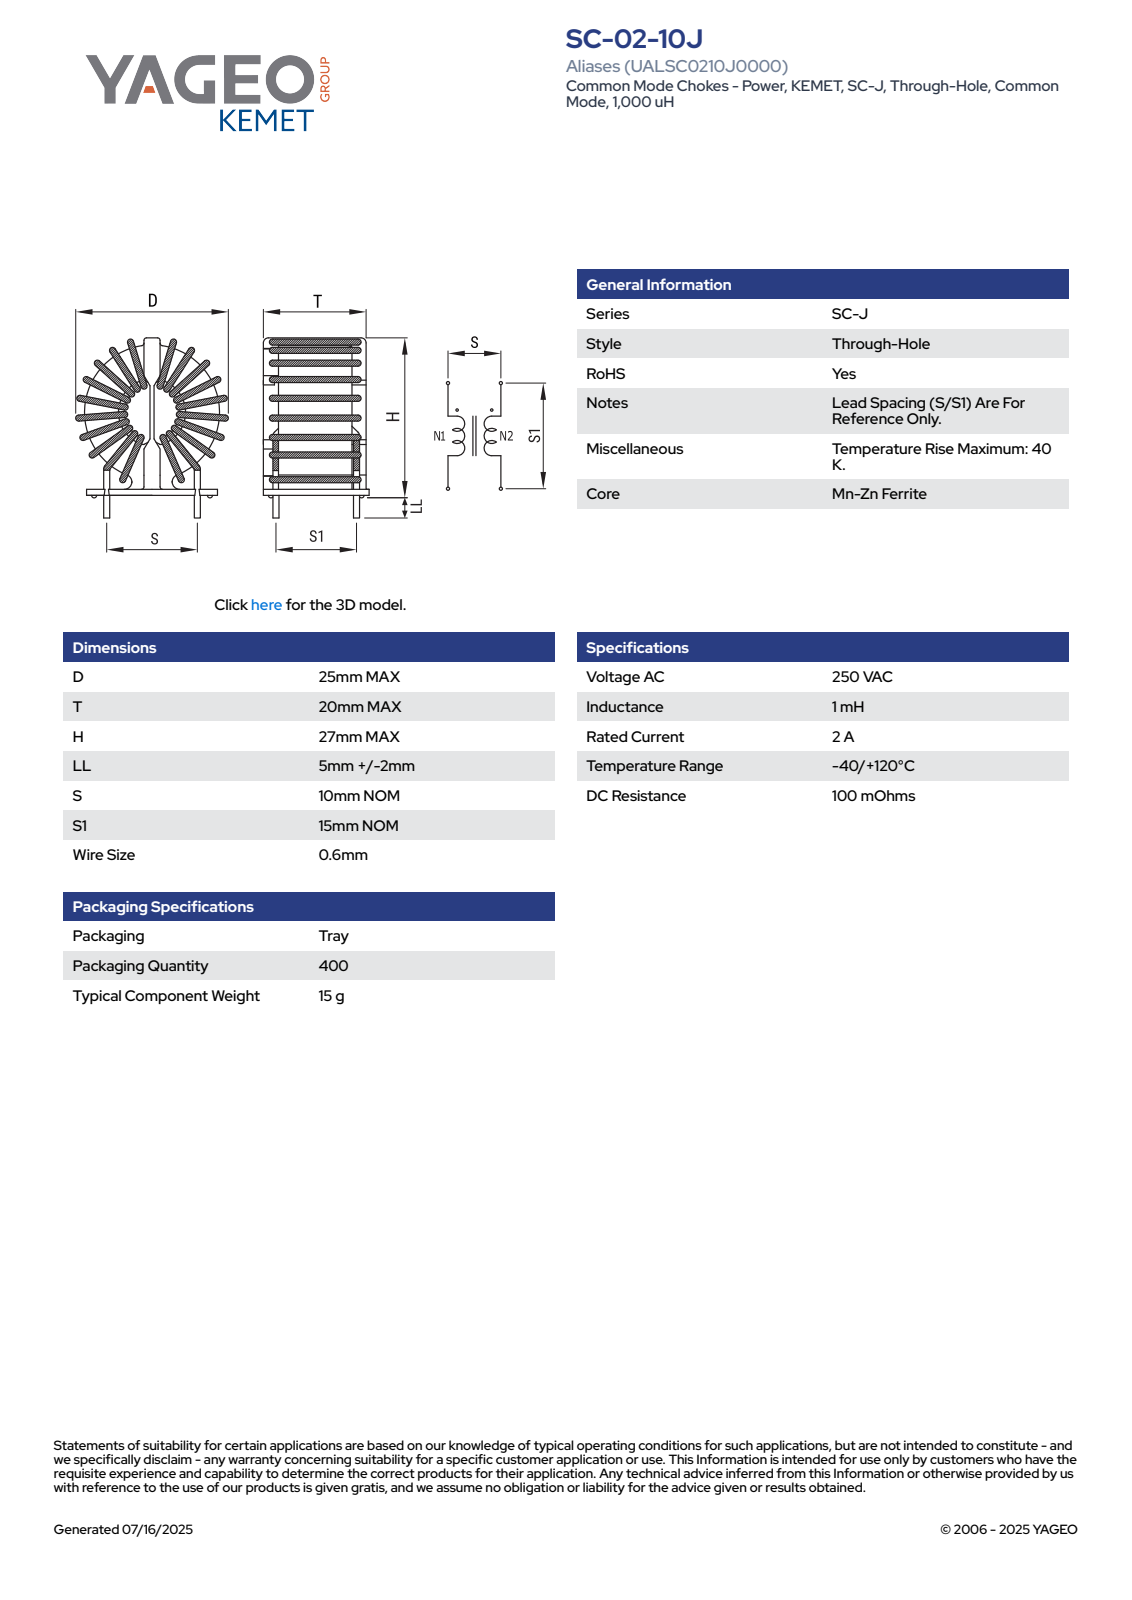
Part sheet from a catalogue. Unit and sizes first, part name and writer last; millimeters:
Units: millimetres
Overall size (bounding box): 31.5 × 25 × 20
Round bosses / shafts (diameter × count): ⌀0.6 ×8, ⌀1 ×4
Partial cylindrical surfaces — rounded edges, fillets, slot ends (radius × count): R0.5 ×21, R0.3 ×16, R1 ×6, R0.42 ×4, R1.5 ×4, R0.9 ×2, R3.09 ×1, R4.39 ×1
Main face-to-face distances: 2.35, 19, 1.2, 2, 3.2, 0.8, 12.6, 0.5, 19.5, 9.4
Volume: 9 040 mm³ · Surface area: 4 710 mm²
Bodies: 1 solid, 334 faces (141 planar, 113 cylindrical, 80 other)
Part name (STEP PRODUCT): SC-02-10J
STEP written by: SolidWorks 2018 (AUTOMOTIVE_DESIGN)
